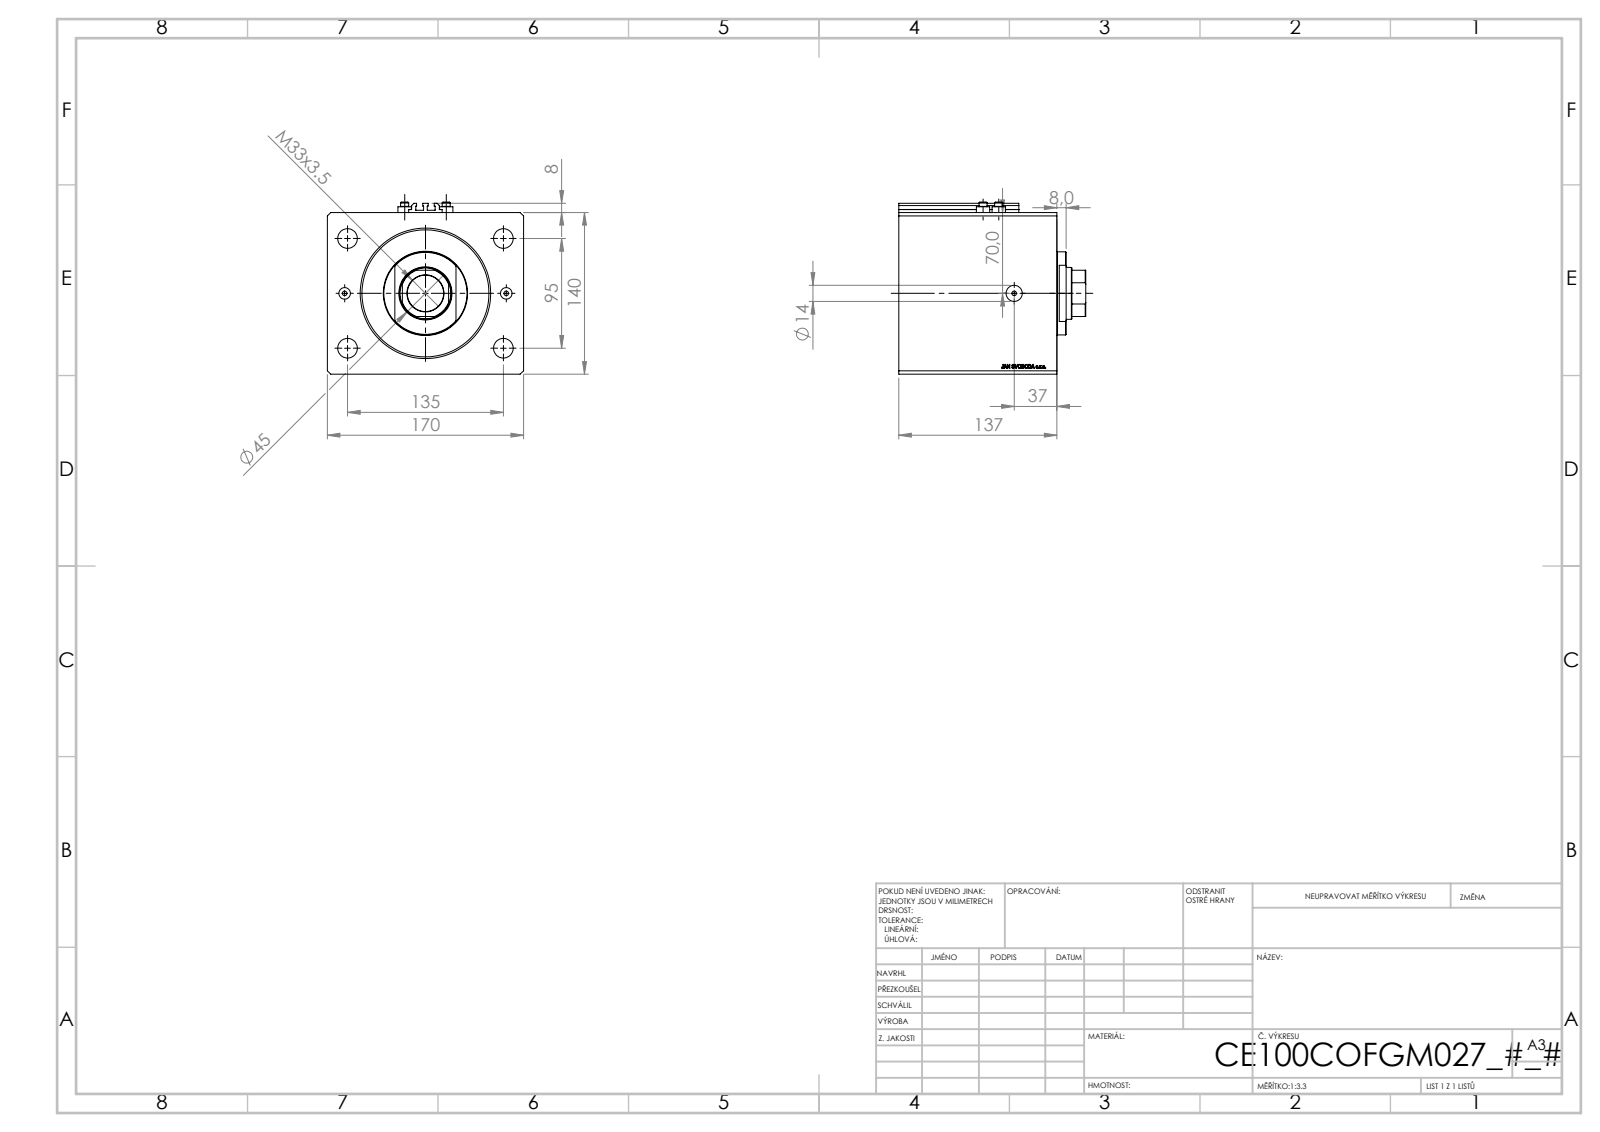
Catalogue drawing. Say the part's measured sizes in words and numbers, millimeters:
The part is named "V250CE_C_Body; ALLEN BOLT V250CE; V250CE_C_VCP; V250CE_VC_C". Its 3-D file was written by "SolidWorks 2019 (CONFIG_CONTROL_DESIGN)". It is 8 solids with 1034 faces: 504 planar, 86 cylindrical and 444 other. Overall it measures 170 by 162 by 149 millimeters. Its volume is 2 985 000 cubic millimeters and its surface area 290 764 square millimeters. Round holes: 8 of diameter 4, 4 of diameter 17, 2 of diameter 10, 2 of diameter 14, 1 of diameter 31.5, 1 of diameter 45, 1 of diameter 100, 1 of diameter 113. Round bosses or shafts: 4 of diameter 11.6, 4 of diameter 7, 1 of diameter 72. Partial cylindrical surfaces (rounded edges, fillets, slot ends): 10 of radius 0.2, 1 of radius 22. The main face-to-face distances are 140, 170, 137, 28.9, 108.1, 25, 112, 83.1, 27, 52. The hole center spacings are 47.57, 82.54, 145.47, 13.6, 36, 38.48, 70, 95.
